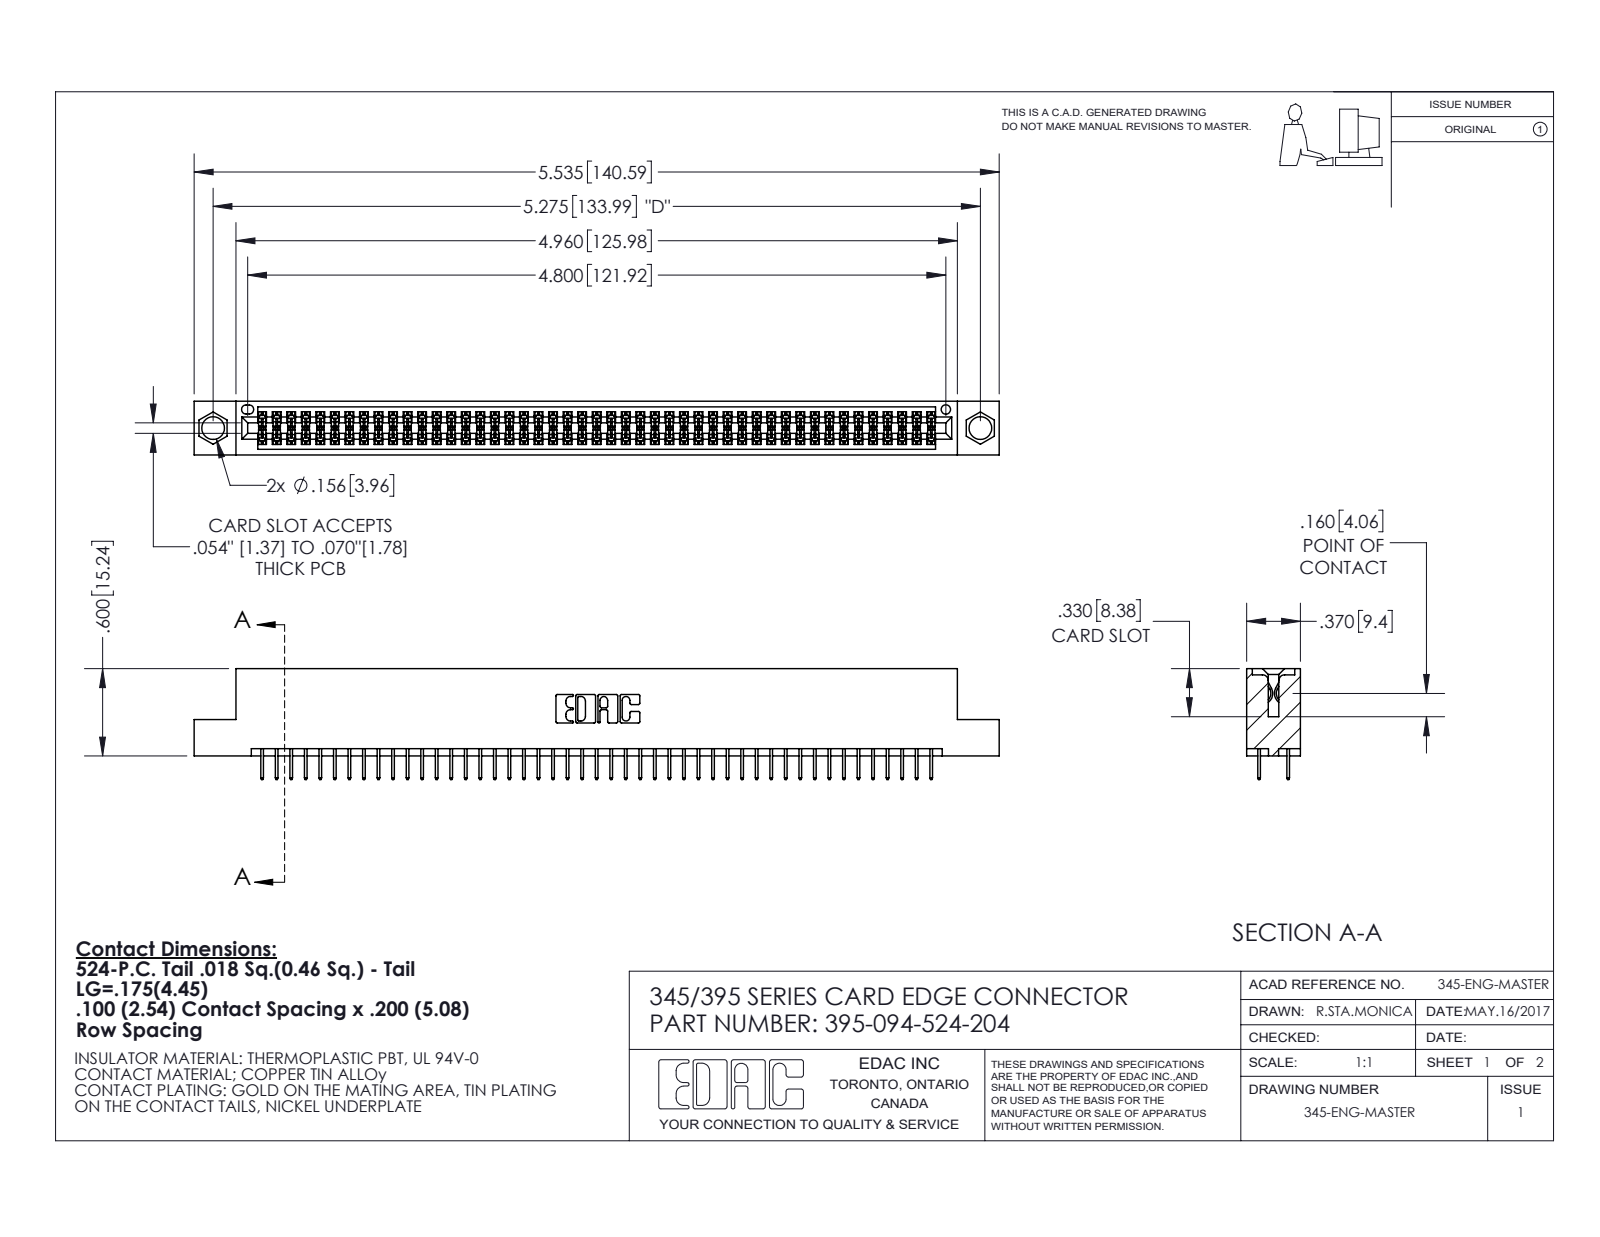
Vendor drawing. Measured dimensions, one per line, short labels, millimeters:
name: 345-292-001_345-293-124; 395-094-524-204; 345 Part_Flush Mounting Lugs - 0.156 Dia-TI
written by: SolidWorks 2020 (CONFIG_CONTROL_DESIGN)
unit: mm
bodies: 95 solids, 5216 faces (3760 planar, 1456 cylindrical, 0 other)
size: 140.6 × 19.4 × 9.4
volume: 13 500 mm³; area: 19 460 mm²
holes: 2× ⌀4, 1× ⌀1.6
rounds: 187× R0.2, 22× R0.3, 6× R0.2, 6× R0.8, 3× R0.7, 2× R0.4, 2× R0.5, 2× R0.6
face distances: 1.8, 7.6, 5.1, 9.4, 2.5, 6.9, 0.6, 5.7, 1.8, 4.4
hole spacings: 6.9, 128, 134
